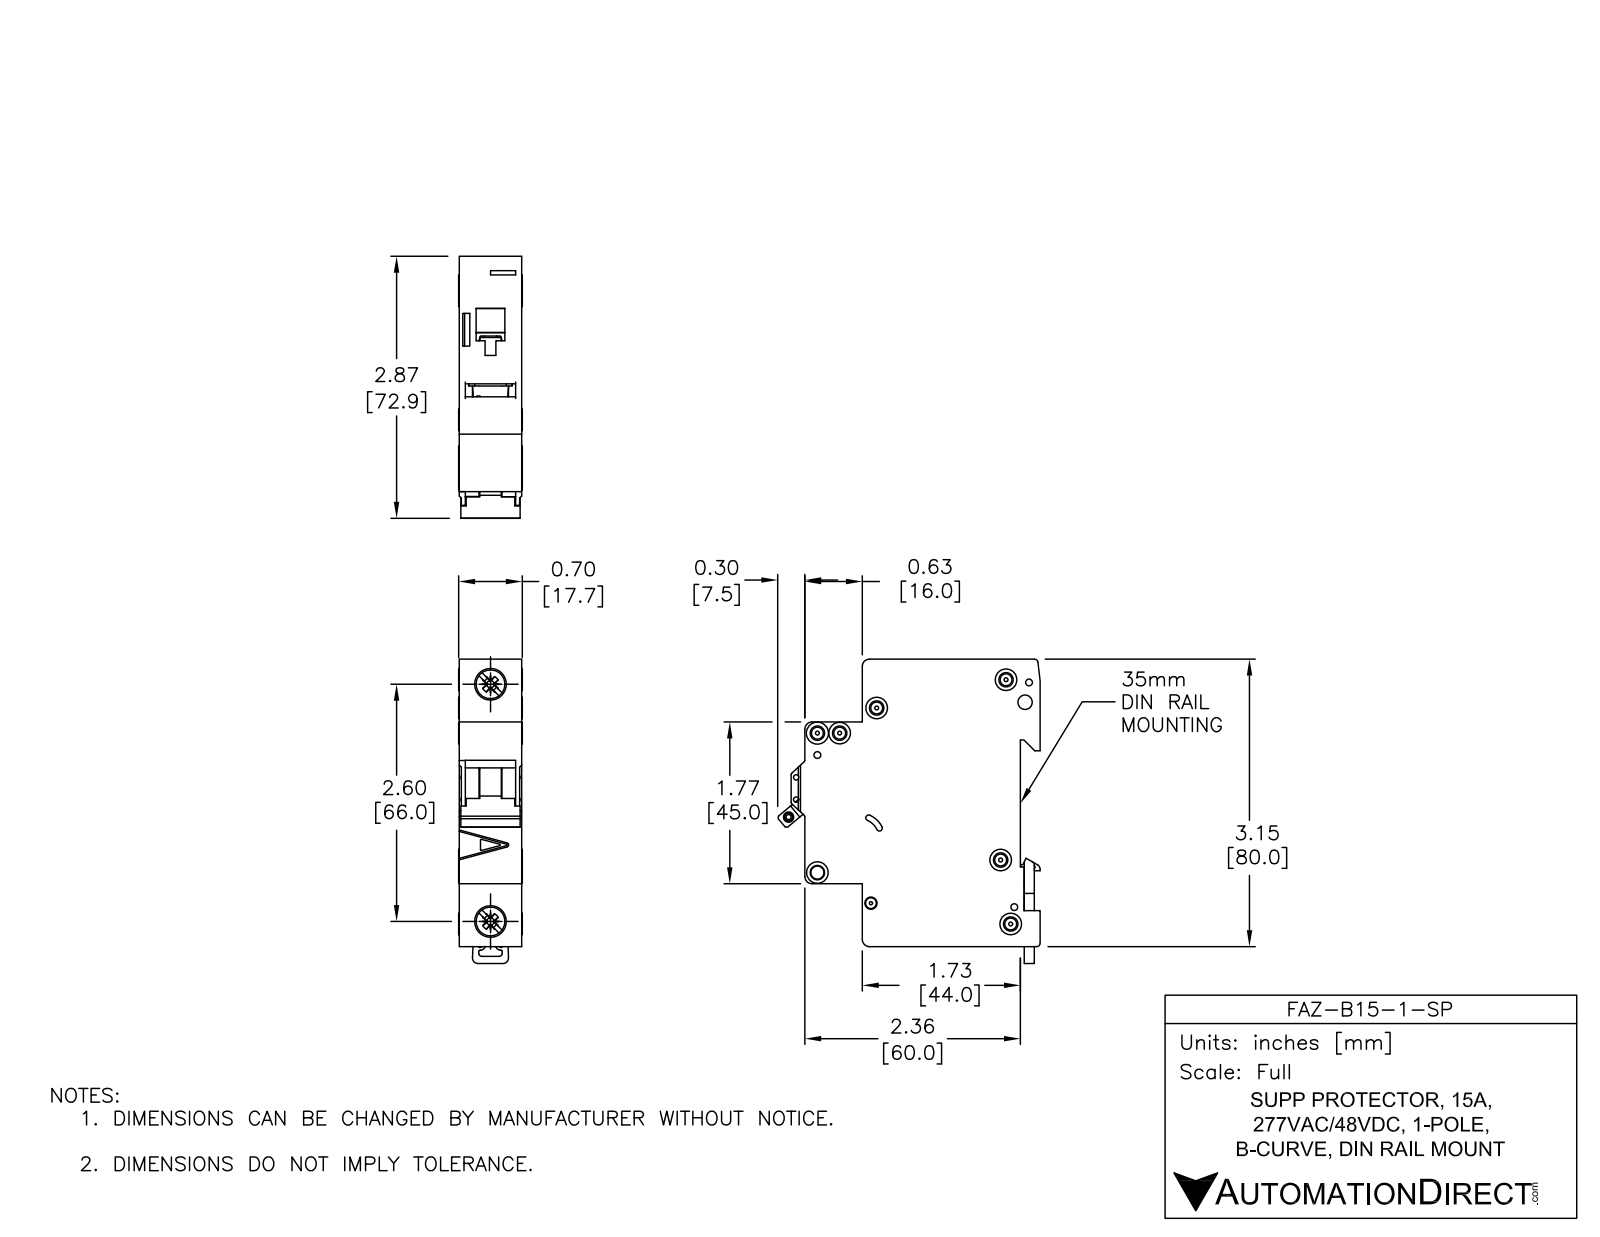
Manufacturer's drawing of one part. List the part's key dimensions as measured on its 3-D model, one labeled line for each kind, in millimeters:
Part name (STEP PRODUCT): FAZ-B15-1-SP
STEP written by: SolidWorks 2014 (AUTOMOTIVE_DESIGN)
Units: millimetres
Bodies: 5 solids, 558 faces (235 planar, 202 cylindrical, 121 other)
Overall size (bounding box): 84.78 × 73.04 × 17.7
Volume: 74 935 mm³ · Surface area: 19 545 mm²
Round holes (diameter × count): ⌀3.6 ×6, ⌀1.9 ×3, ⌀1.09 ×2, ⌀1.5 ×2, ⌀4 ×2, ⌀7.15 ×2, ⌀2.15 ×1, ⌀2.2 ×1, ⌀2.55 ×1, ⌀3.3 ×1, ⌀3.4 ×1
Round bosses / shafts (diameter × count): ⌀6 ×4, ⌀8.2 ×2, ⌀2.5 ×1
Partial cylindrical surfaces — rounded edges, fillets, slot ends (radius × count): R0.25 ×30, R0.5 ×13, R2 ×8, R0.2 ×5, R1 ×4, R0.8 ×2, R3 ×2, R1.5 ×1
Main face-to-face distances: 17.5, 79.48, 5.5, 49.5, 44, 65.5, 60, 16, 1.75, 15.75
Hole centre spacings: 6.2, 13.64, 4.81, 5.19, 5.61, 6.1, 6.44, 8.19
